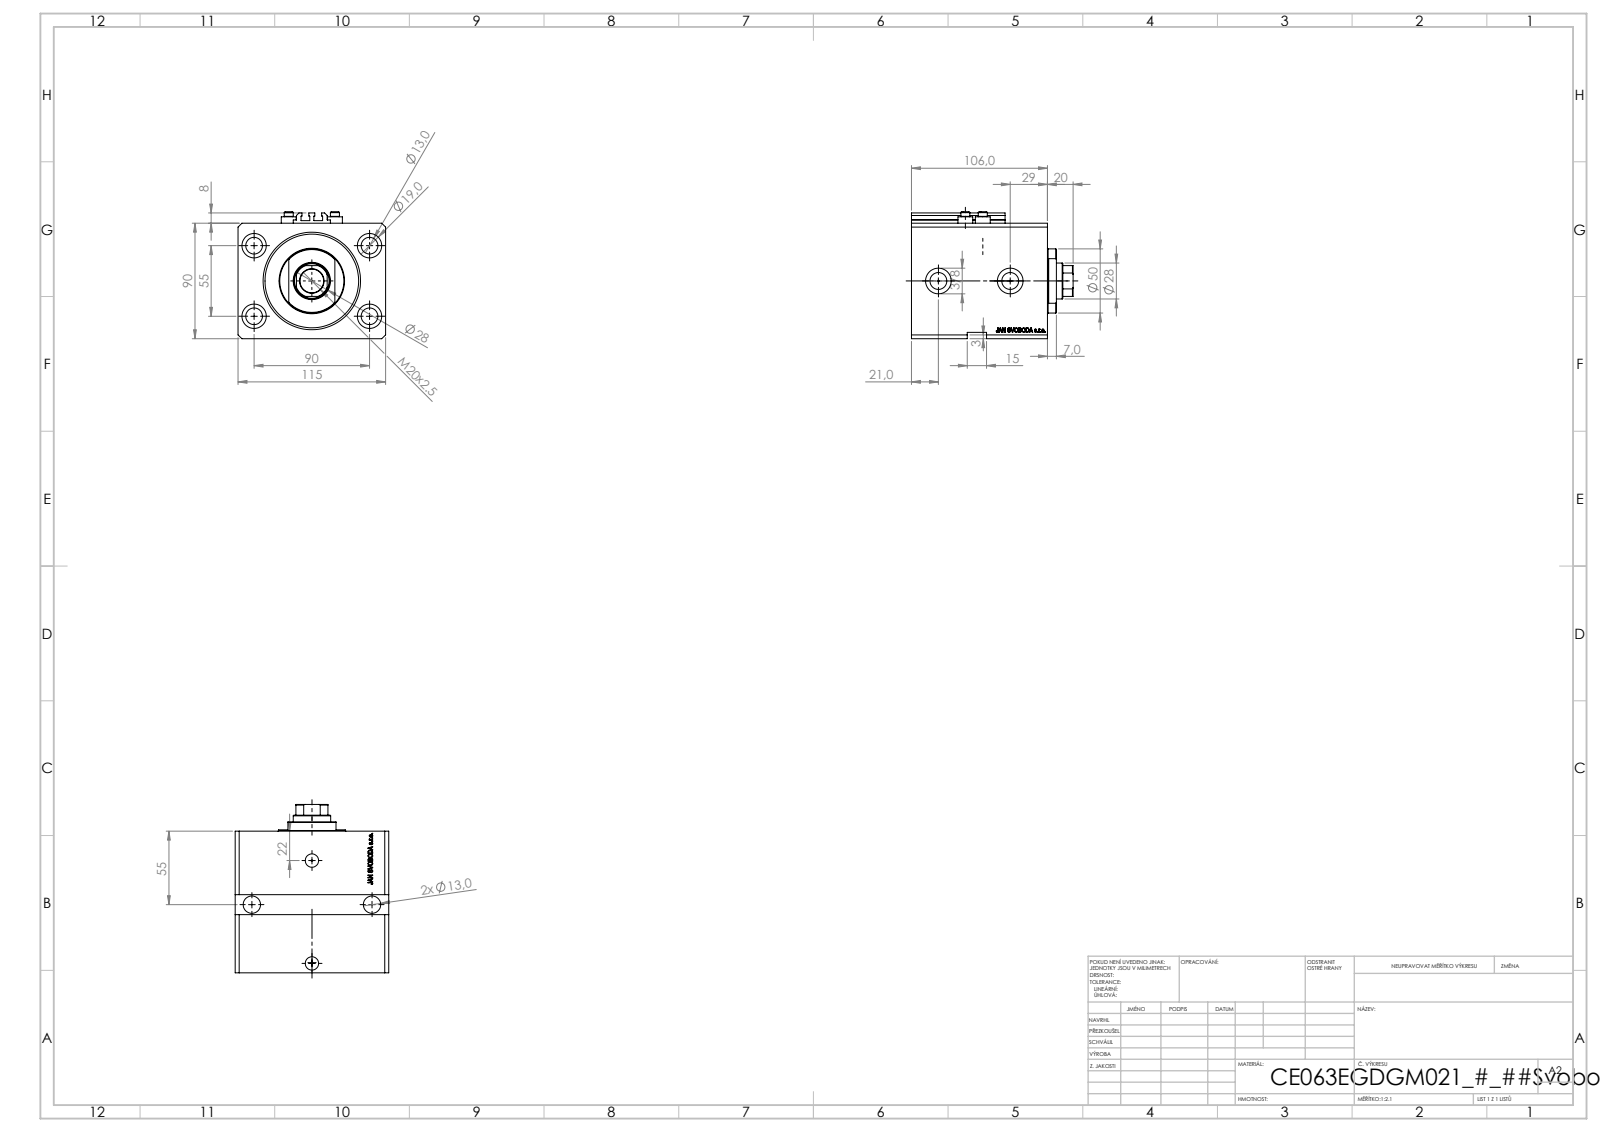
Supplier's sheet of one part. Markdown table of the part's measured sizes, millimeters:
| quantity | value |
| --- | --- |
| part name | V250CE_C_VCP; V250CE_VC_E; V250CE_E_Body; ALLEN BOLT V250CE |
| STEP written by | SolidWorks 2019 (CONFIG_CONTROL_DESIGN) |
| units | millimeters |
| bodies | 8 solids, 1123 faces (547 planar, 138 cylindrical, 438 other) |
| overall size | 126 × 115 × 99 |
| volume | 958 363 mm³ |
| surface area | 156 086 mm² |
| round holes (diameter × count) | 13 × 6, 1.25 × 4, 4 × 4, 19 × 4, 10 × 2, 13.16 × 2, 20 × 2, 18.5 × 1, 28 × 1, 63 × 1, 76 × 1 |
| round bosses / shafts (diameter × count) | 11.6 × 4, 7 × 4, 50 × 1 |
| partial cylindrical surfaces (radius × count) | 0.2 × 10, 13.5 × 1 |
| main face-to-face distances | 90, 115, 106, 88.1, 20, 17.9, 86, 68.1, 21, 65 |
| hole center spacings | 52.74, 90, 13.6, 27.39, 28.46, 33.62, 36, 38.48 |
